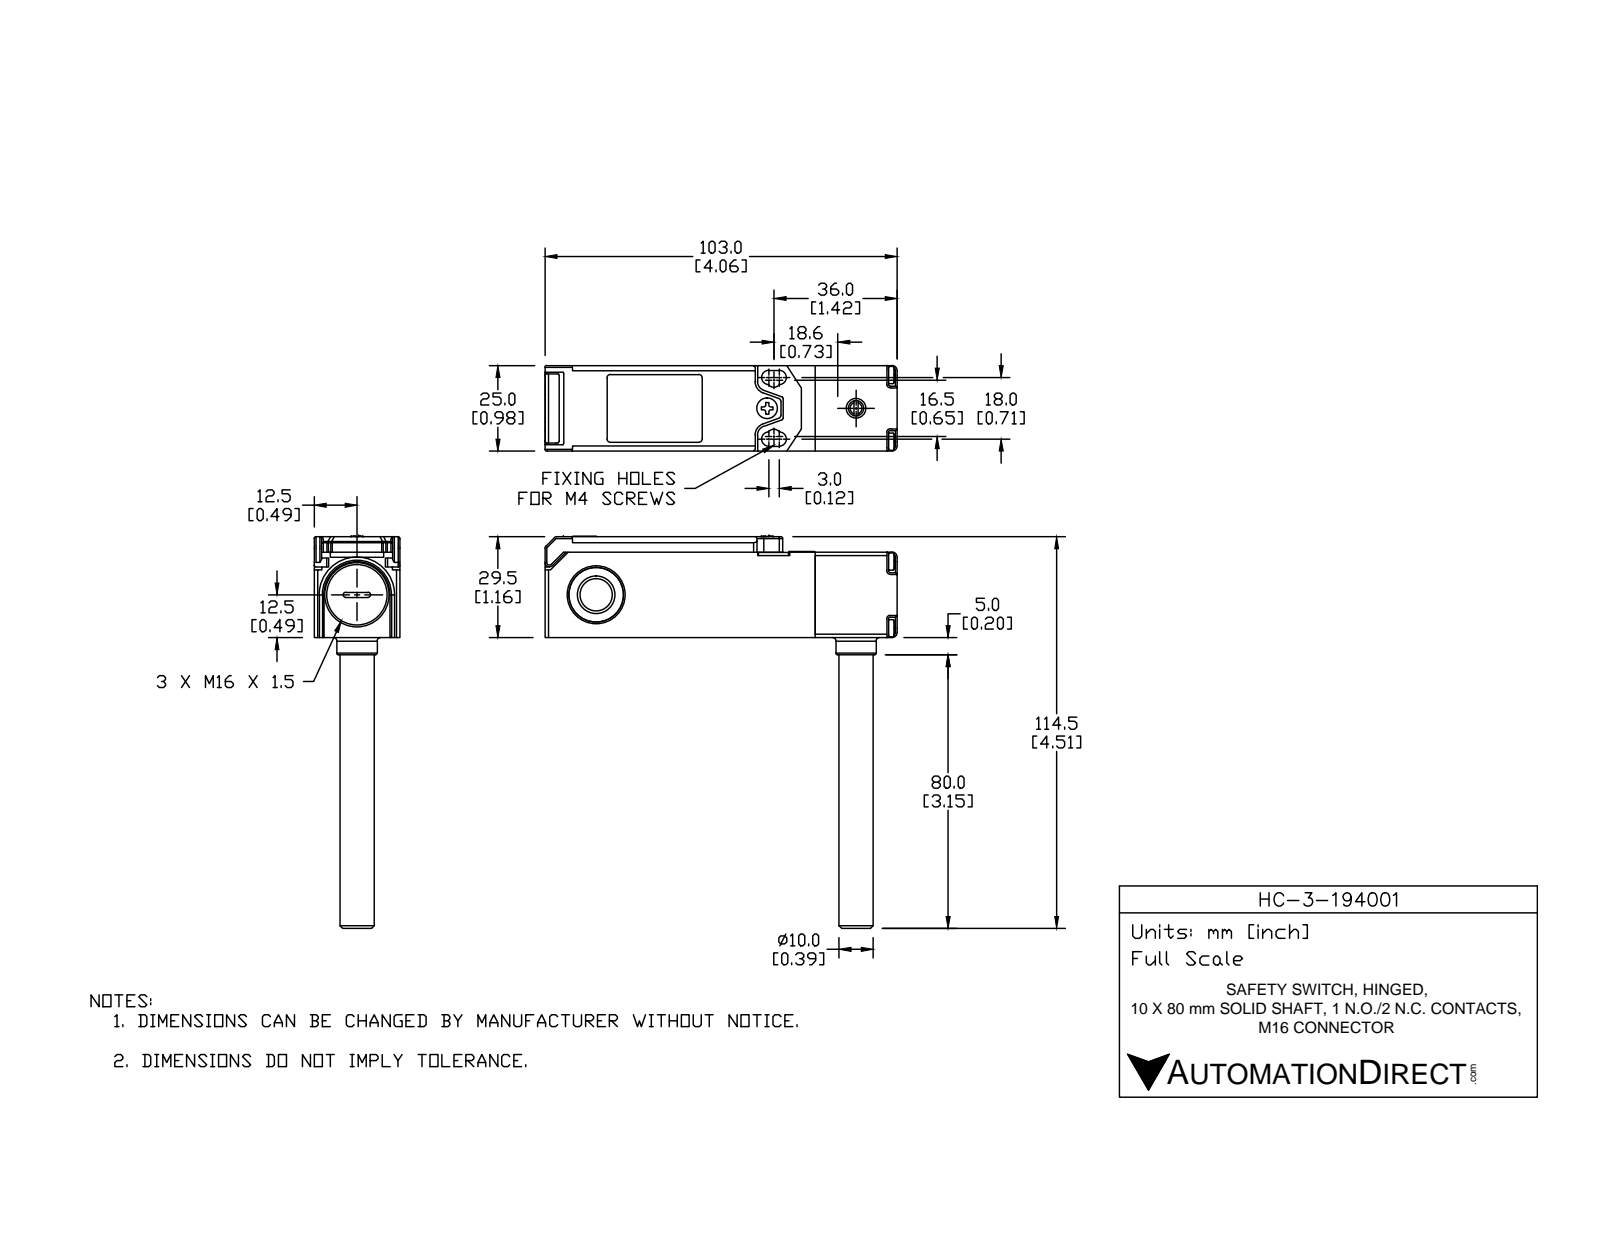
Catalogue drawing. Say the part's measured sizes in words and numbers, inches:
The part is named "HC-3-194001". Its 3-D file was written by "SolidWorks 2014 (AUTOMOTIVE_DESIGN)". It is 13 solids with 1848 faces: 866 planar, 583 cylindrical and 399 other. Overall it measures 4.517 by 4.055 by 0.984 inches. Its volume is 2.231 cubic inches and its surface area 52.85 square inches. Round holes: 5 of diameter 0.126, 4 of diameter 0.094, 2 of diameter 0.059, 2 of diameter 0.063, 2 of diameter 0.071, 2 of diameter 0.087, 2 of diameter 0.142, 2 of diameter 0.63, 1 of diameter 0.055, 1 of diameter 0.081, 1 of diameter 0.098, 1 of diameter 0.102. Round bosses or shafts: 5 of diameter 0.102, 4 of diameter 0.197, 4 of diameter 0.079, 2 of diameter 0.138, 1 of diameter 0.394, 1 of diameter 0.386, 1 of diameter 0.256, 1 of diameter 0.228. Partial cylindrical surfaces (rounded edges, fillets, slot ends): 225 of radius 0.02, 24 of radius 0.004, 21 of radius 0.039, 12 of radius 0.012, 6 of radius 0.059, 6 of radius 0.083, 6 of radius 0.11, 6 of radius 0.138. The main face-to-face distances are 0.984, 0.079, 0.071, 0.913, 0.177, 0.906, 0.098, 0.039, 0.827, 0.087. The hole center spacings are 0.543, 0.768, 0.171, 0.187, 0.245, 0.414, 0.423, 0.426.
